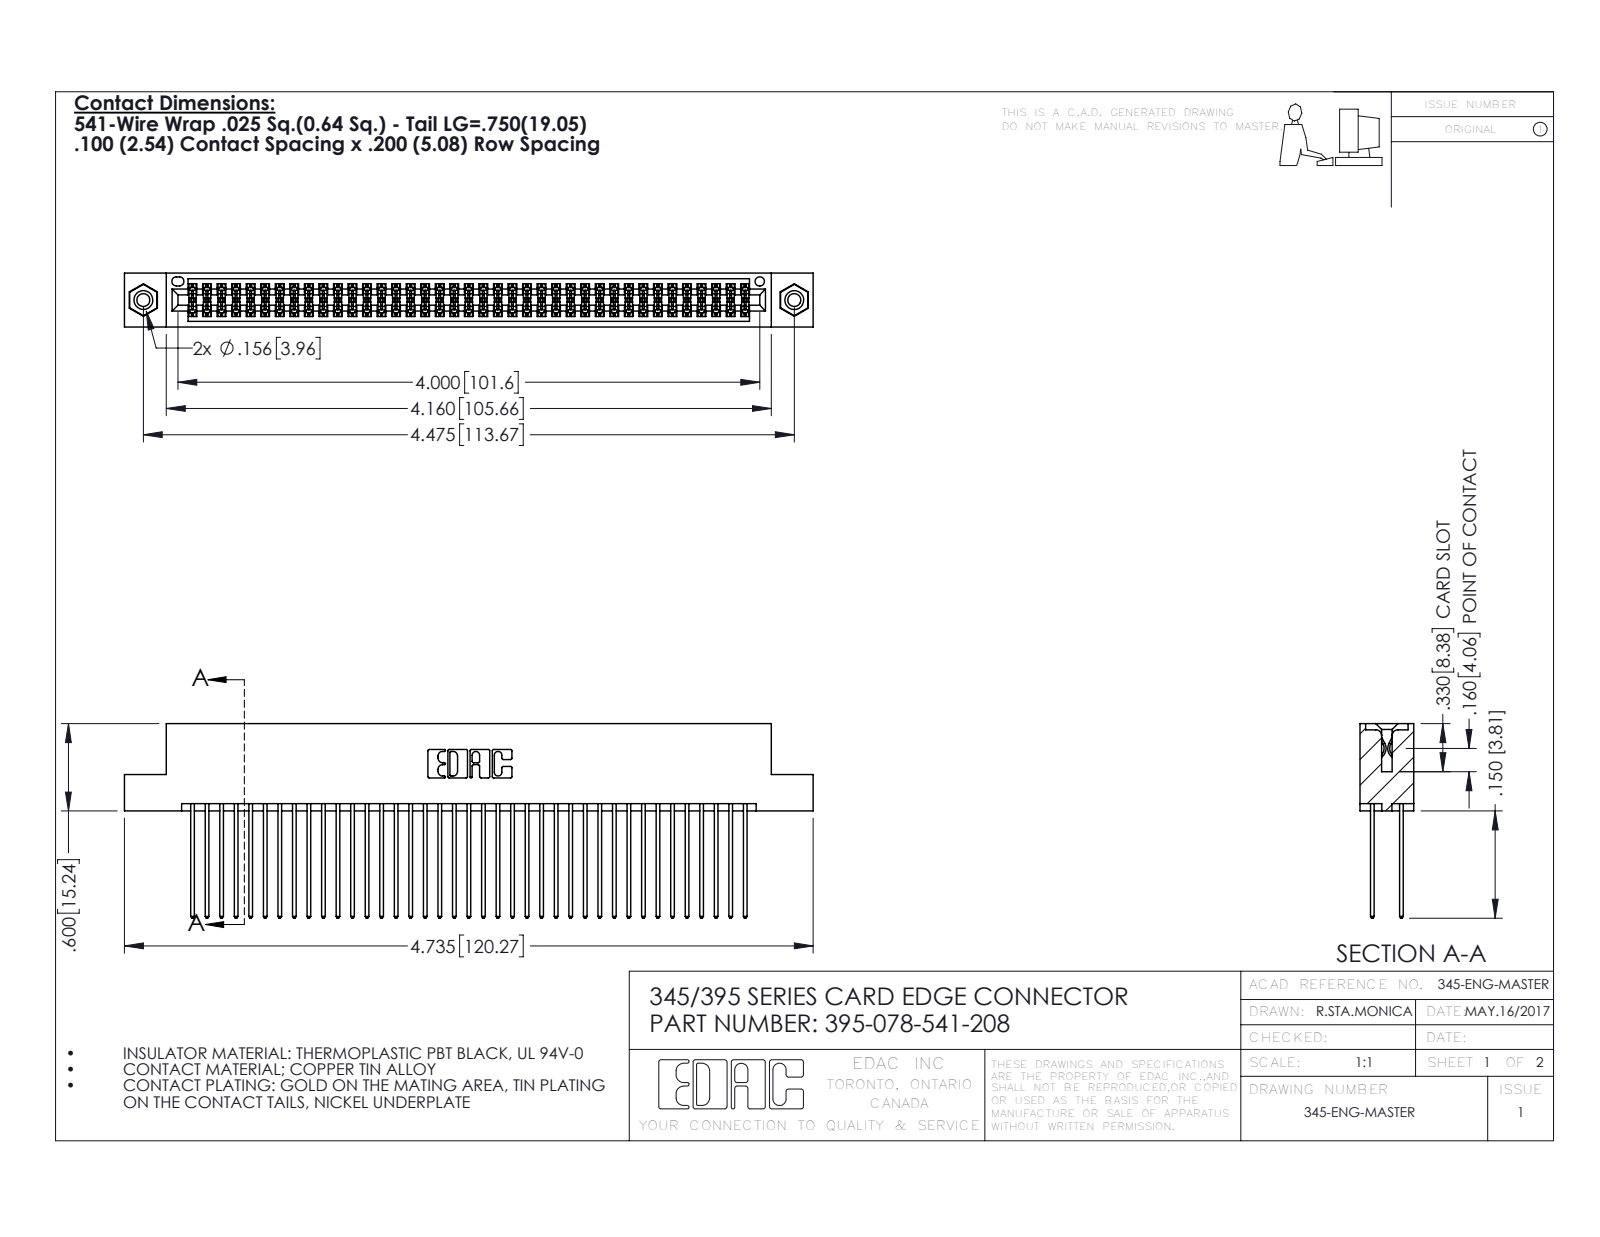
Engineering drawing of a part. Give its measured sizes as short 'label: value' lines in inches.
name: 345-292-001_345-293-141; 395-078-541-208; 345-250-001_345-250-003-102; 345 Part_Flush Mounting Lugs - 0.156 Dia-TI
written by: SolidWorks 2016 (CONFIG_CONTROL_DESIGN)
unit: in
bodies: 81 solids, 4086 faces (2686 planar, 1384 cylindrical, 16 other)
size: 4.735 × 1.337 × 0.37
volume: 0.738 in³; area: 30.91 in²
holes: 2× ⌀0.089, 2× ⌀0.125, 2× ⌀0.156, 1× ⌀0.064
bosses: 2× ⌀0.155
rounds: 117× R0.006, 78× R0.01, 22× R0.01, 6× R0.007, 6× R0.031, 3× R0.026, 2× R0.014, 2× R0.019
face distances: 0.072, 0.298, 0.2, 0.098, 0.272, 0.025, 0.225, 0.37, 0.175, 0.149
hole spacings: 0.27, 4.239, 4.475
